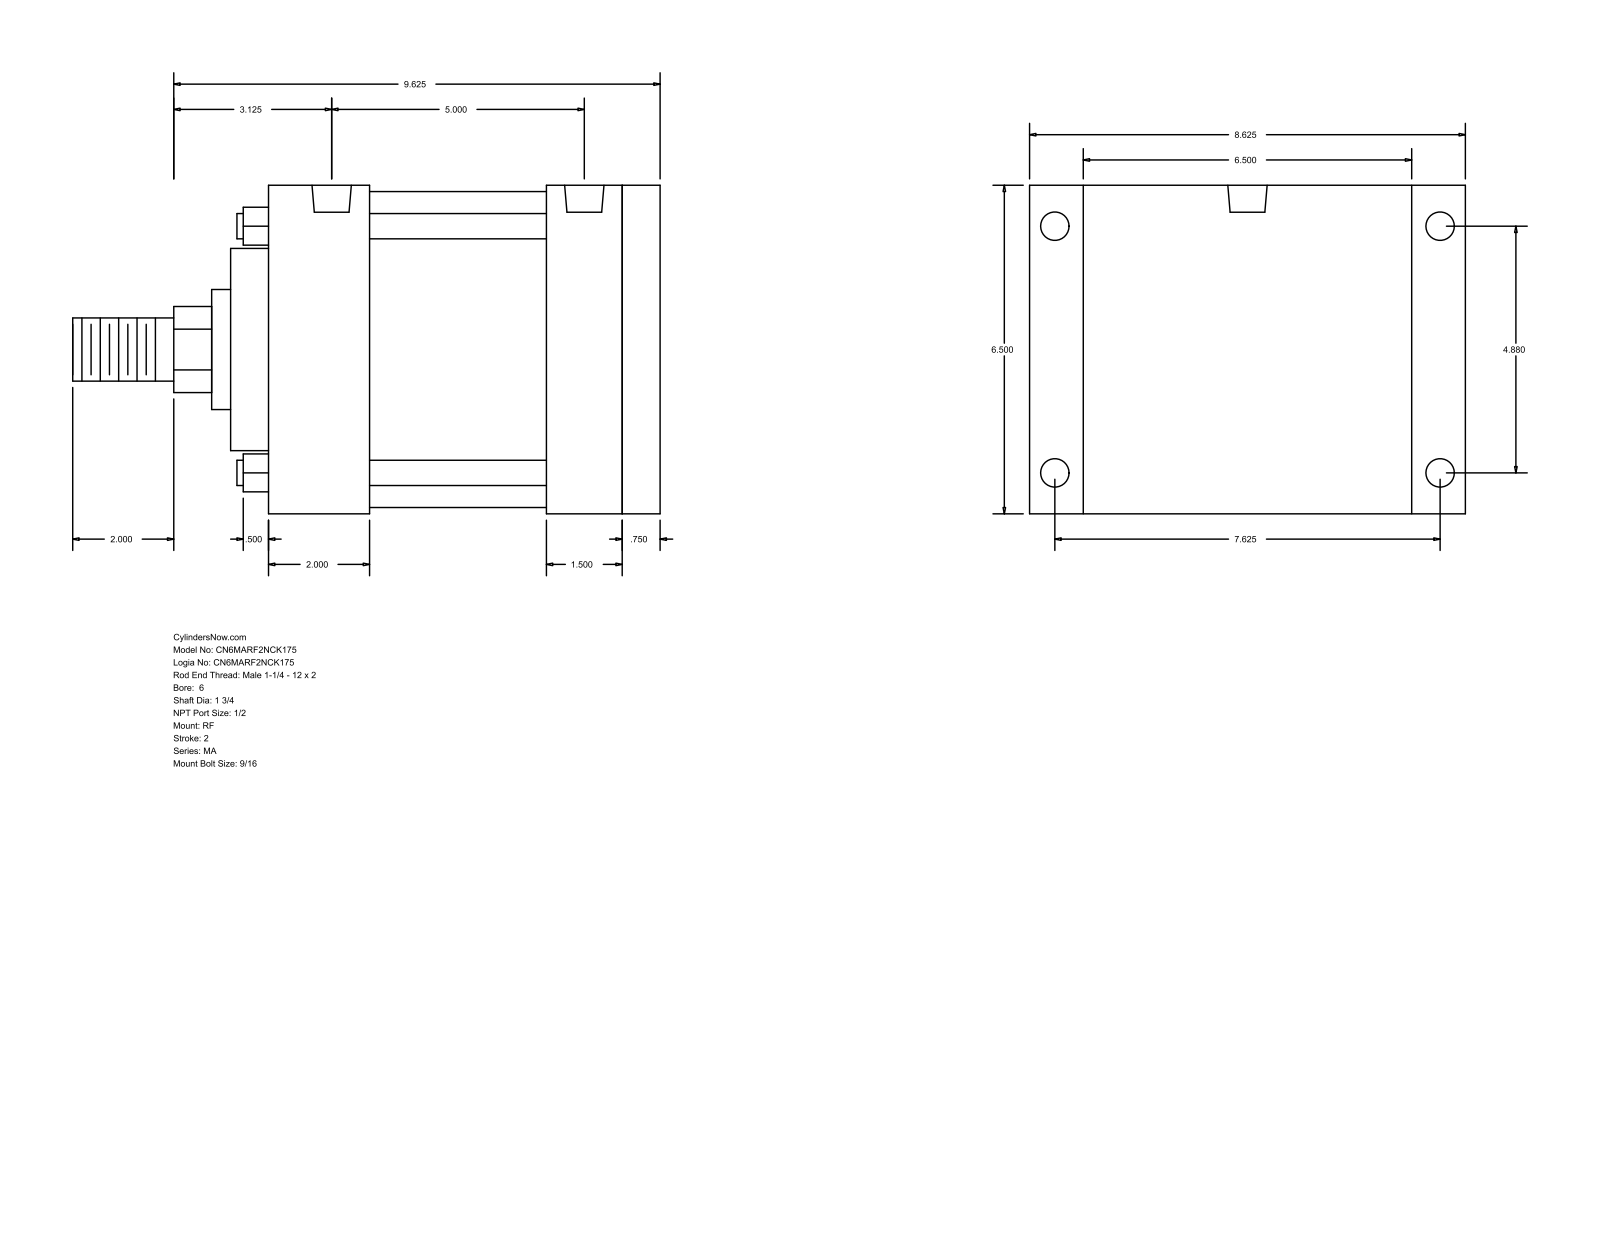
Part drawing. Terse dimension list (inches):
name: MA_RF__0600_1.75
written by: GSSL Pune (CONFIG_CONTROL_DESIGN)
unit: in
bodies: 0 solids, 94 faces (65 planar, 29 cylindrical, 0 other)
size: 11.625 × 8.625 × 6.5
holes: 4× ⌀0.563, 4× ⌀0.687, 2× ⌀0.778
bosses: 4× ⌀0.5, 1× ⌀6.25, 1× ⌀4, 1× ⌀2.375, 1× ⌀1.75, 1× ⌀1.25
rounds: 1× R0.852
face distances: 6.5, 7.75, 0.75, 7, 2, 0.75, 5, 5.75, 5.5, 3.5
hole spacings: 4.88, 5, 7.625, 9.053
